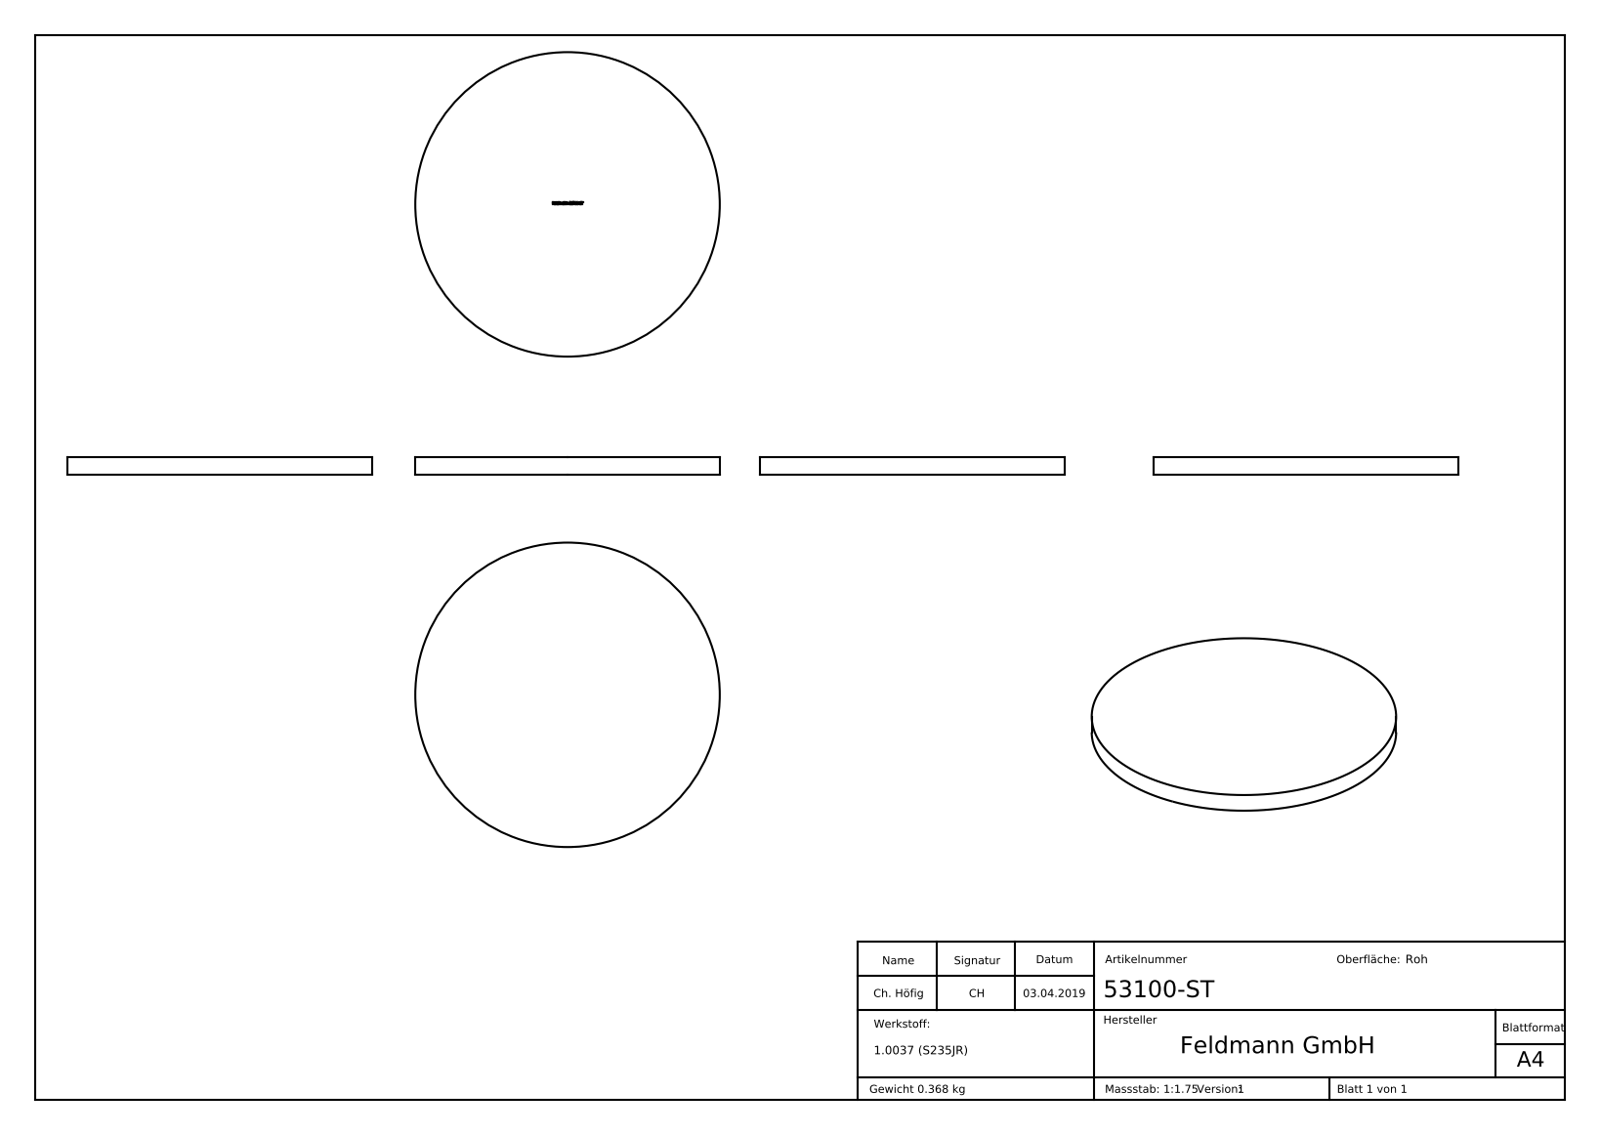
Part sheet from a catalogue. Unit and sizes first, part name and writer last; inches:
Units: inches
Overall size (bounding box): 3.937 × 3.937 × 0.236
Round bosses / shafts (diameter × count): ⌀3.937 ×1
Main face-to-face distances: 0.236, 0.232, 0.017, 0.031, 0.039, 0.07, 0.23, 0.048, 0.334, 0.105
Volume: 2.876 in³ · Surface area: 27.28 in²
Bodies: 1 solid, 211 faces (106 planar, 2 cylindrical, 103 other)
Part name (STEP PRODUCT): 53100-ST
STEP written by: SolidWorks 2015 (CONFIG_CONTROL_DESIGN)
